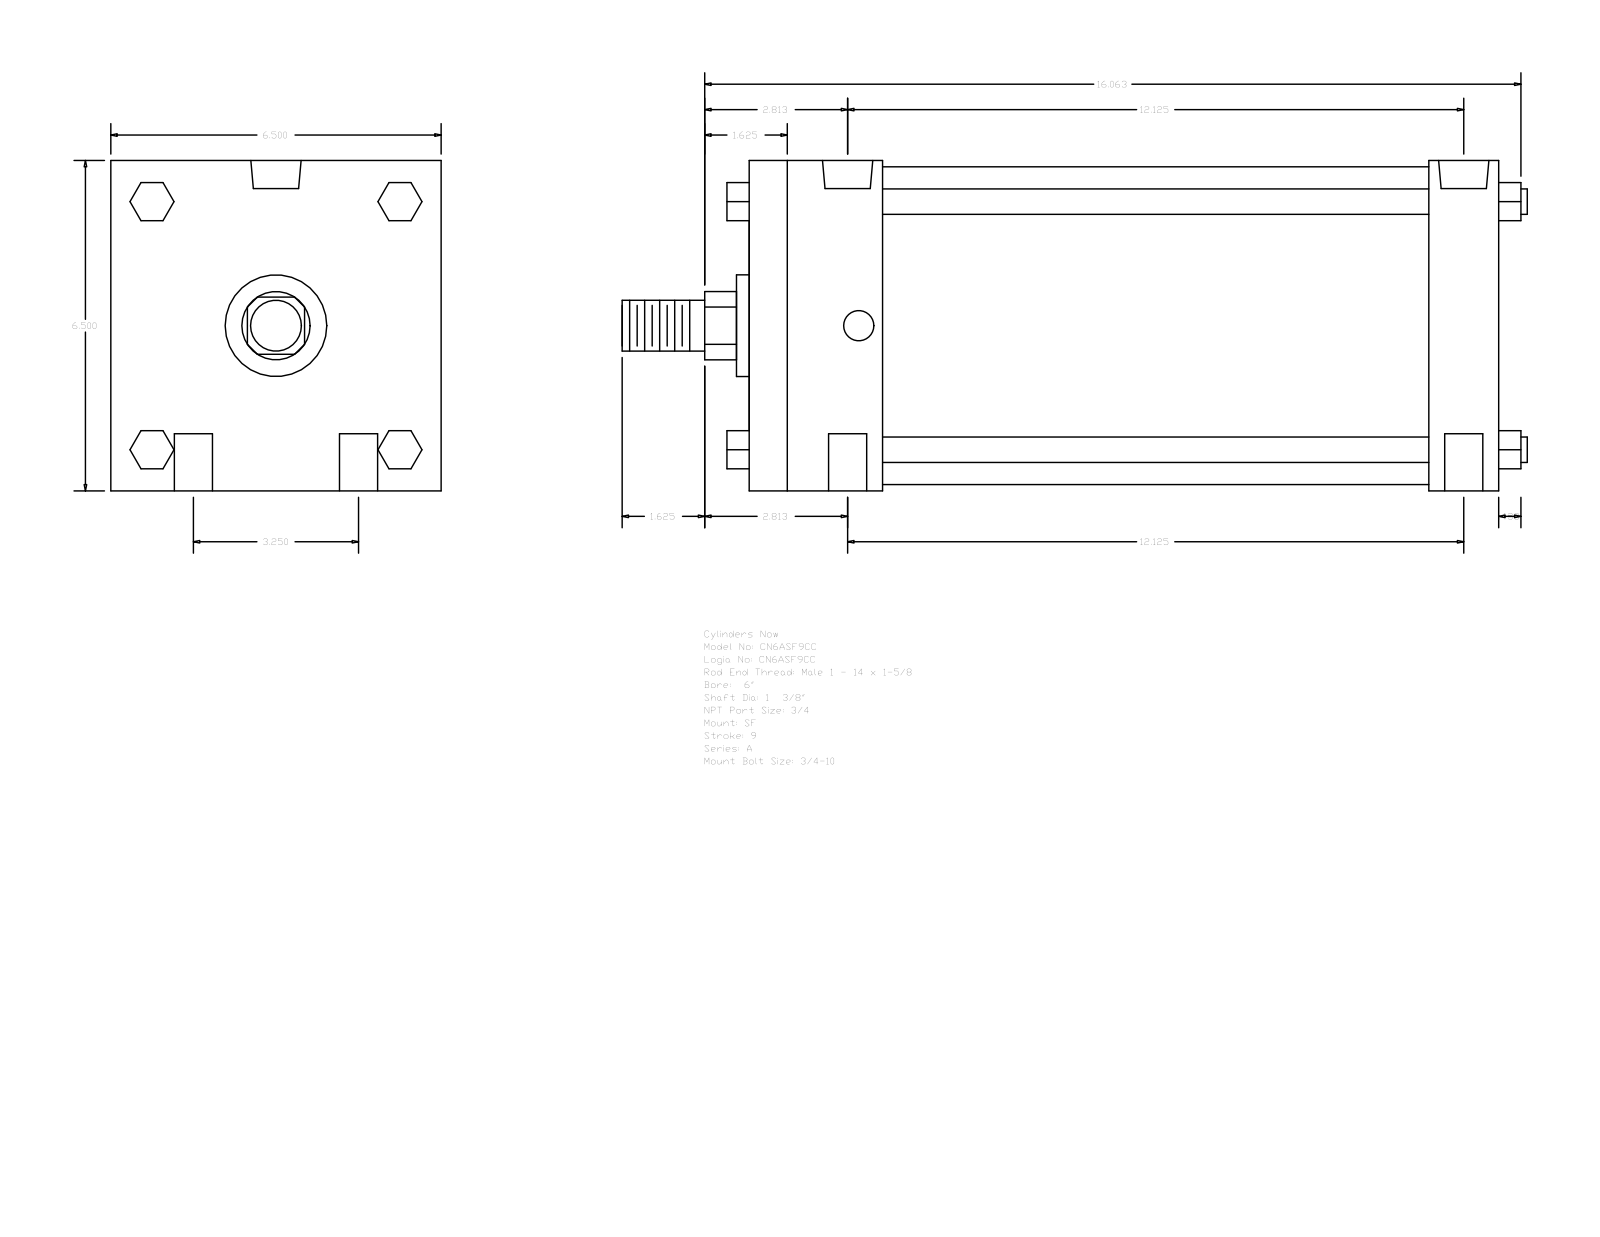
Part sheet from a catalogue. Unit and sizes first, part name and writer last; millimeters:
Units: millimetres
Overall size (bounding box): 452.44 × 165.1 × 165.1
Round holes (diameter × count): ⌀19.05 ×4, ⌀15.08 ×2, ⌀25.12 ×2
Round bosses / shafts (diameter × count): ⌀12.7 ×4, ⌀158.75 ×1, ⌀50.8 ×1, ⌀34.92 ×1, ⌀25.4 ×1
Partial cylindrical surfaces — rounded edges, fillets, slot ends (radius × count): R17.06 ×1
Main face-to-face distances: 165.1, 374.65, 339.72, 34.93, 66.67, 273.05, 307.98, 19.05, 61.97, 107.34
Hole centre spacings: 41.27, 310.72, 307.97, 82.54, 318.84, 296.85
Bodies: 0 solids, 124 faces (94 planar, 30 cylindrical, 0 other)
Part name (STEP PRODUCT): A_SF__0600_1.375
STEP written by: GSSL Pune (CONFIG_CONTROL_DESIGN)
